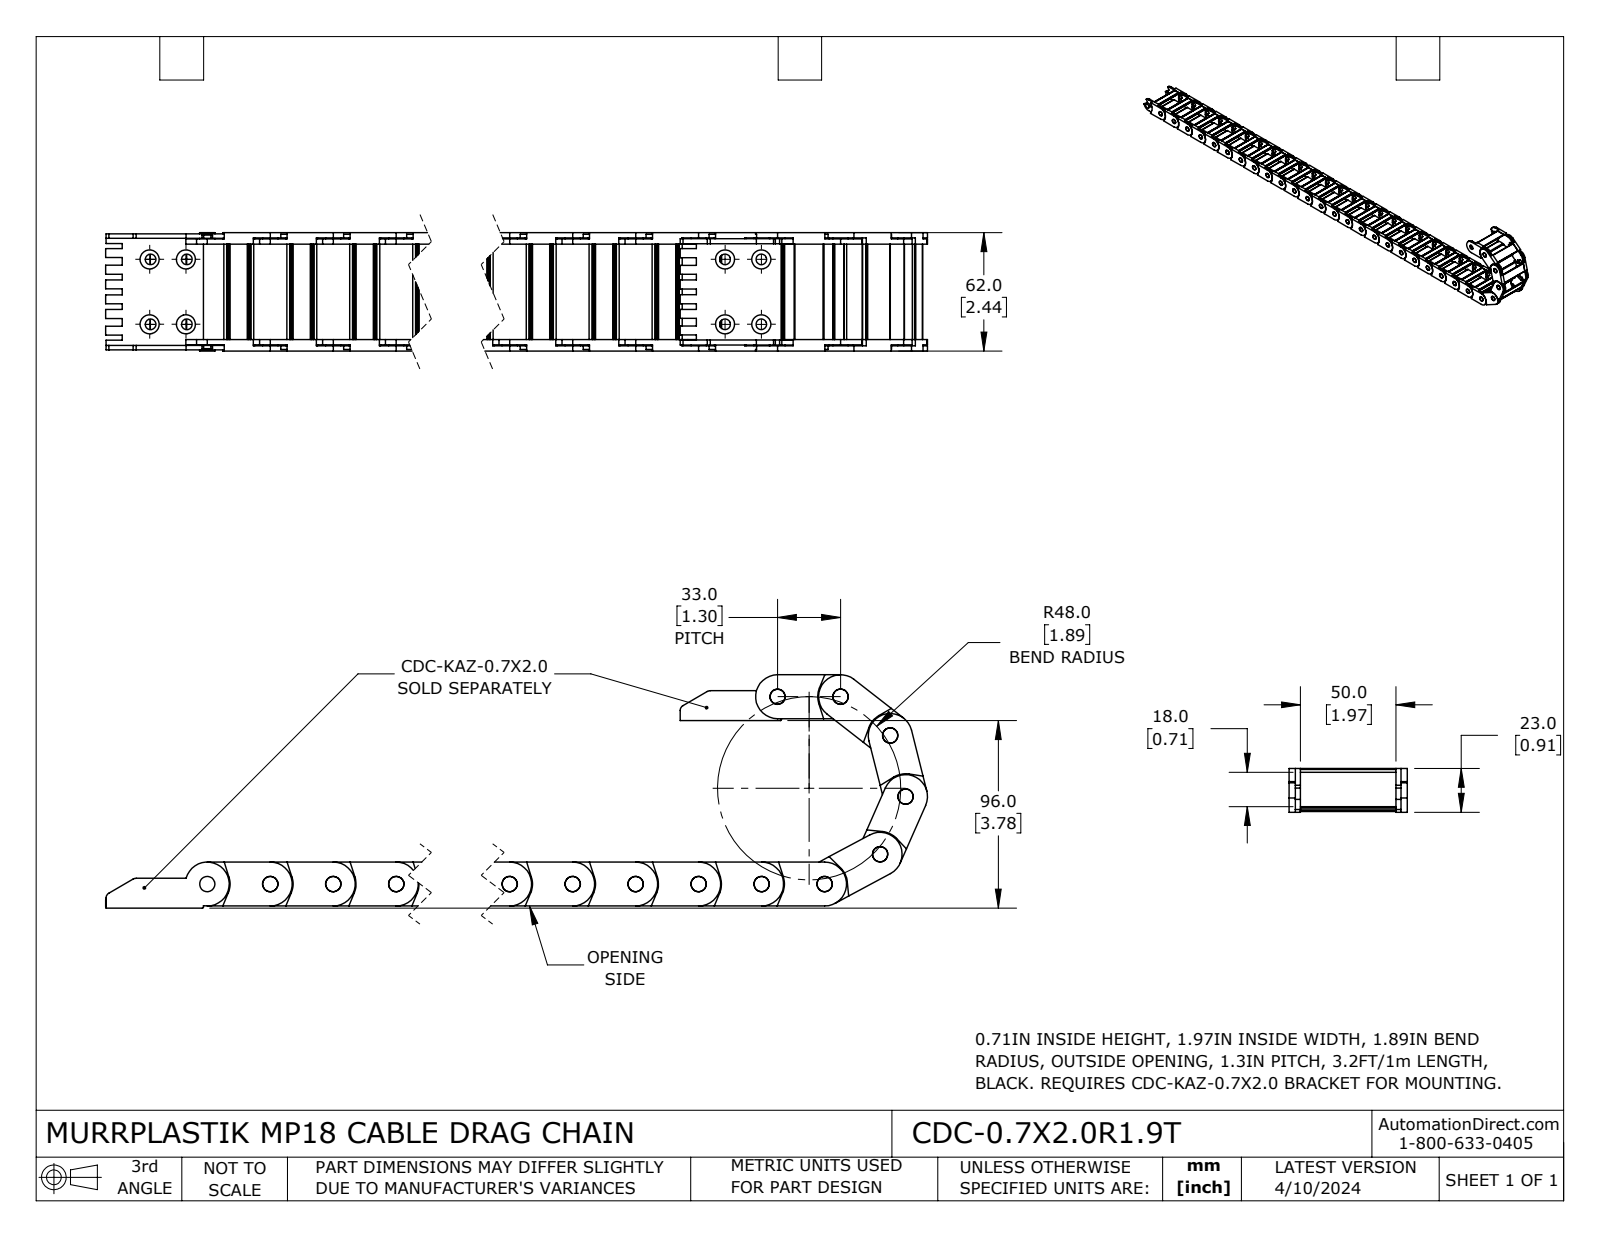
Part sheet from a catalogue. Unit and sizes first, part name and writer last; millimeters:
Units: millimetres
Overall size (bounding box): 890.08 × 121.09 × 62
Round holes (diameter × count): ⌀8 ×30
Round bosses / shafts (diameter × count): ⌀8 ×1
Partial cylindrical surfaces — rounded edges, fillets, slot ends (radius × count): R0.5 ×120, R1.5 ×120, R0.2 ×60, R0.3 ×60, R11.5 ×31, R11.95 ×31, R5 ×30, R5.45 ×30
Main face-to-face distances: 56, 2.7, 3.3, 6, 62, 58.7, 52.7, 59.3, 0.6, 53.3
Hole centre spacings: 33, 66, 99, 132, 165, 198, 231, 264
Volume: 311 252 mm³ · Surface area: 262 185 mm²
Bodies: 30 solids, 2280 faces (1110 planar, 1170 cylindrical, 0 other)
Part name (STEP PRODUCT): CDC-0.7X2.0R1.9T
STEP written by: SolidWorks 2023 (CONFIG_CONTROL_DESIGN)
